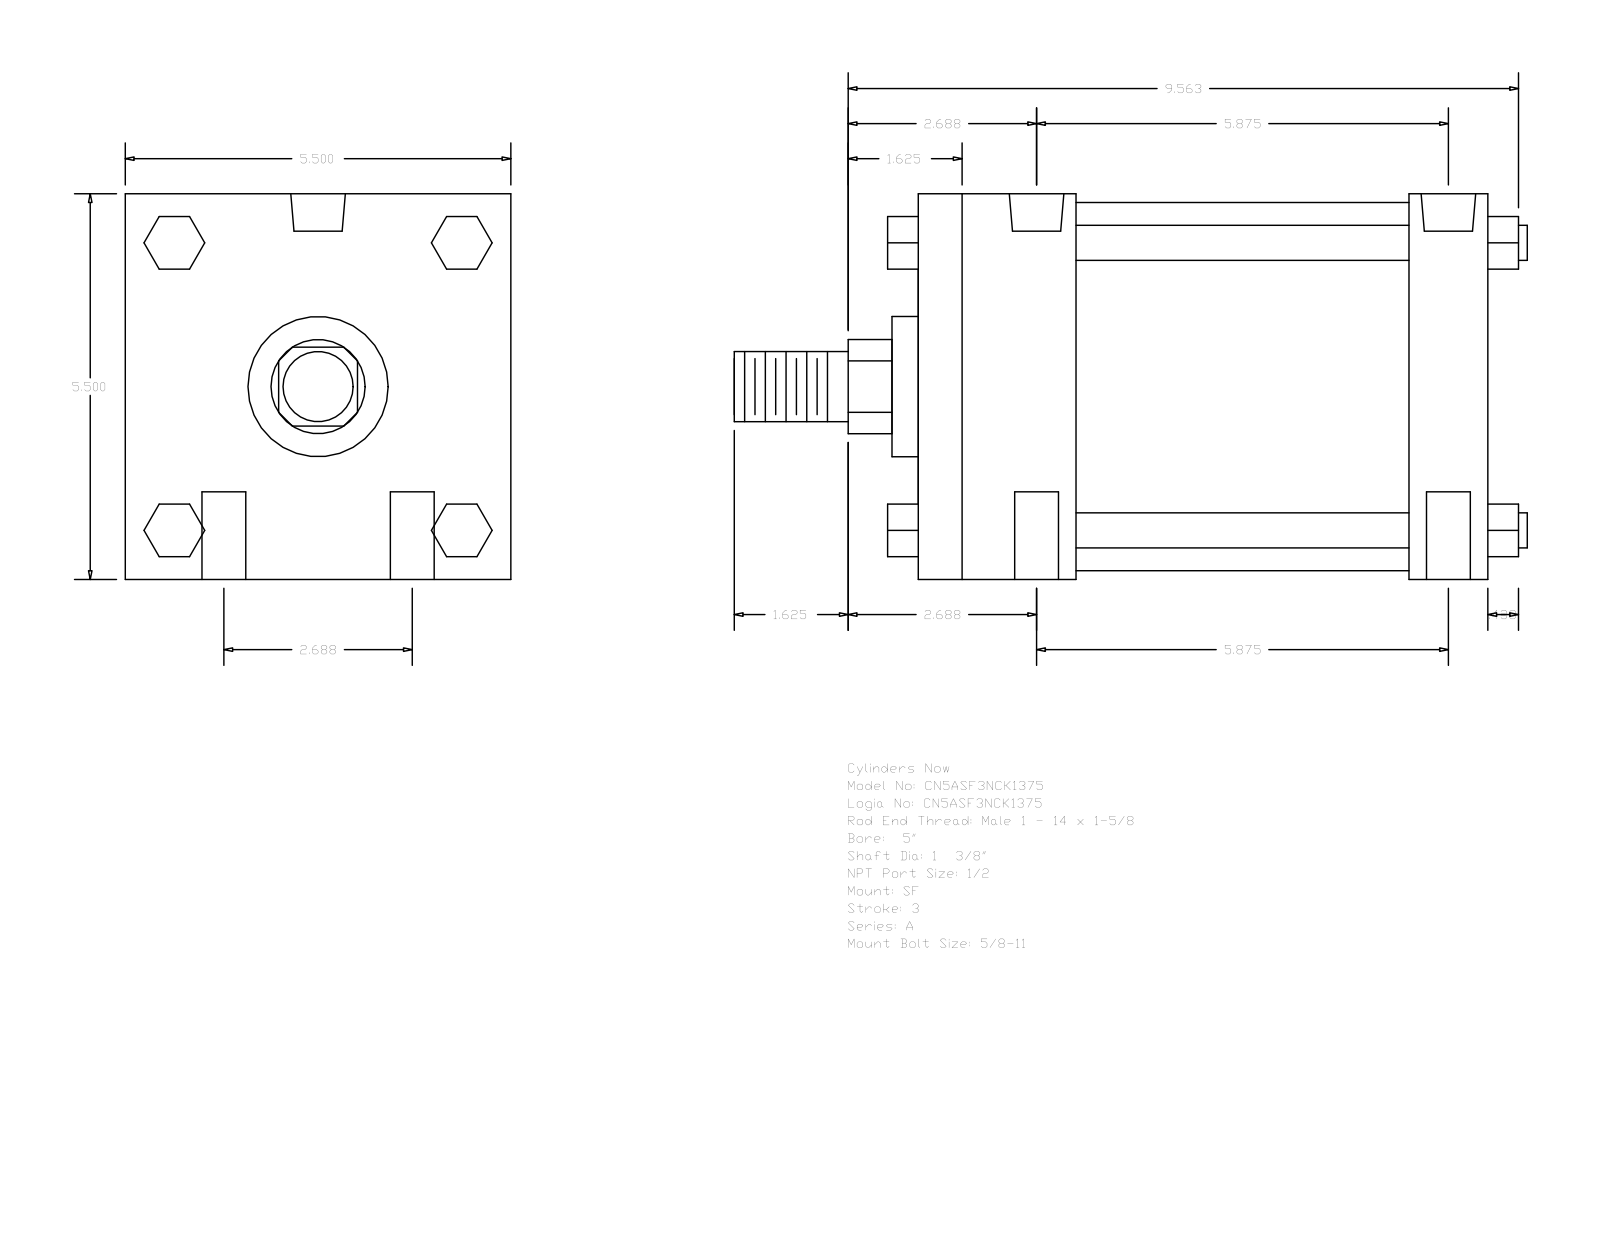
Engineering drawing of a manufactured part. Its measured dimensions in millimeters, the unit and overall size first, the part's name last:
Units: millimetres
Overall size (bounding box): 287.34 × 139.7 × 139.7
Round holes (diameter × count): ⌀15.88 ×4, ⌀8.73 ×2, ⌀19.77 ×2
Round bosses / shafts (diameter × count): ⌀12.7 ×4, ⌀133.35 ×1, ⌀50.8 ×1, ⌀34.92 ×1, ⌀25.4 ×1
Partial cylindrical surfaces — rounded edges, fillets, slot ends (radius × count): R17.06 ×1
Main face-to-face distances: 139.7, 206.38, 57.15, 28.58, 177.8, 120.65, 149.23, 19.05, 52.07, 90.18
Hole centre spacings: 34.13, 153.08, 149.23, 68.26, 164.1, 144.45
Bodies: 0 solids, 124 faces (94 planar, 30 cylindrical, 0 other)
Part name (STEP PRODUCT): A_SF__0500_1.375
STEP written by: GSSL Pune (CONFIG_CONTROL_DESIGN)
